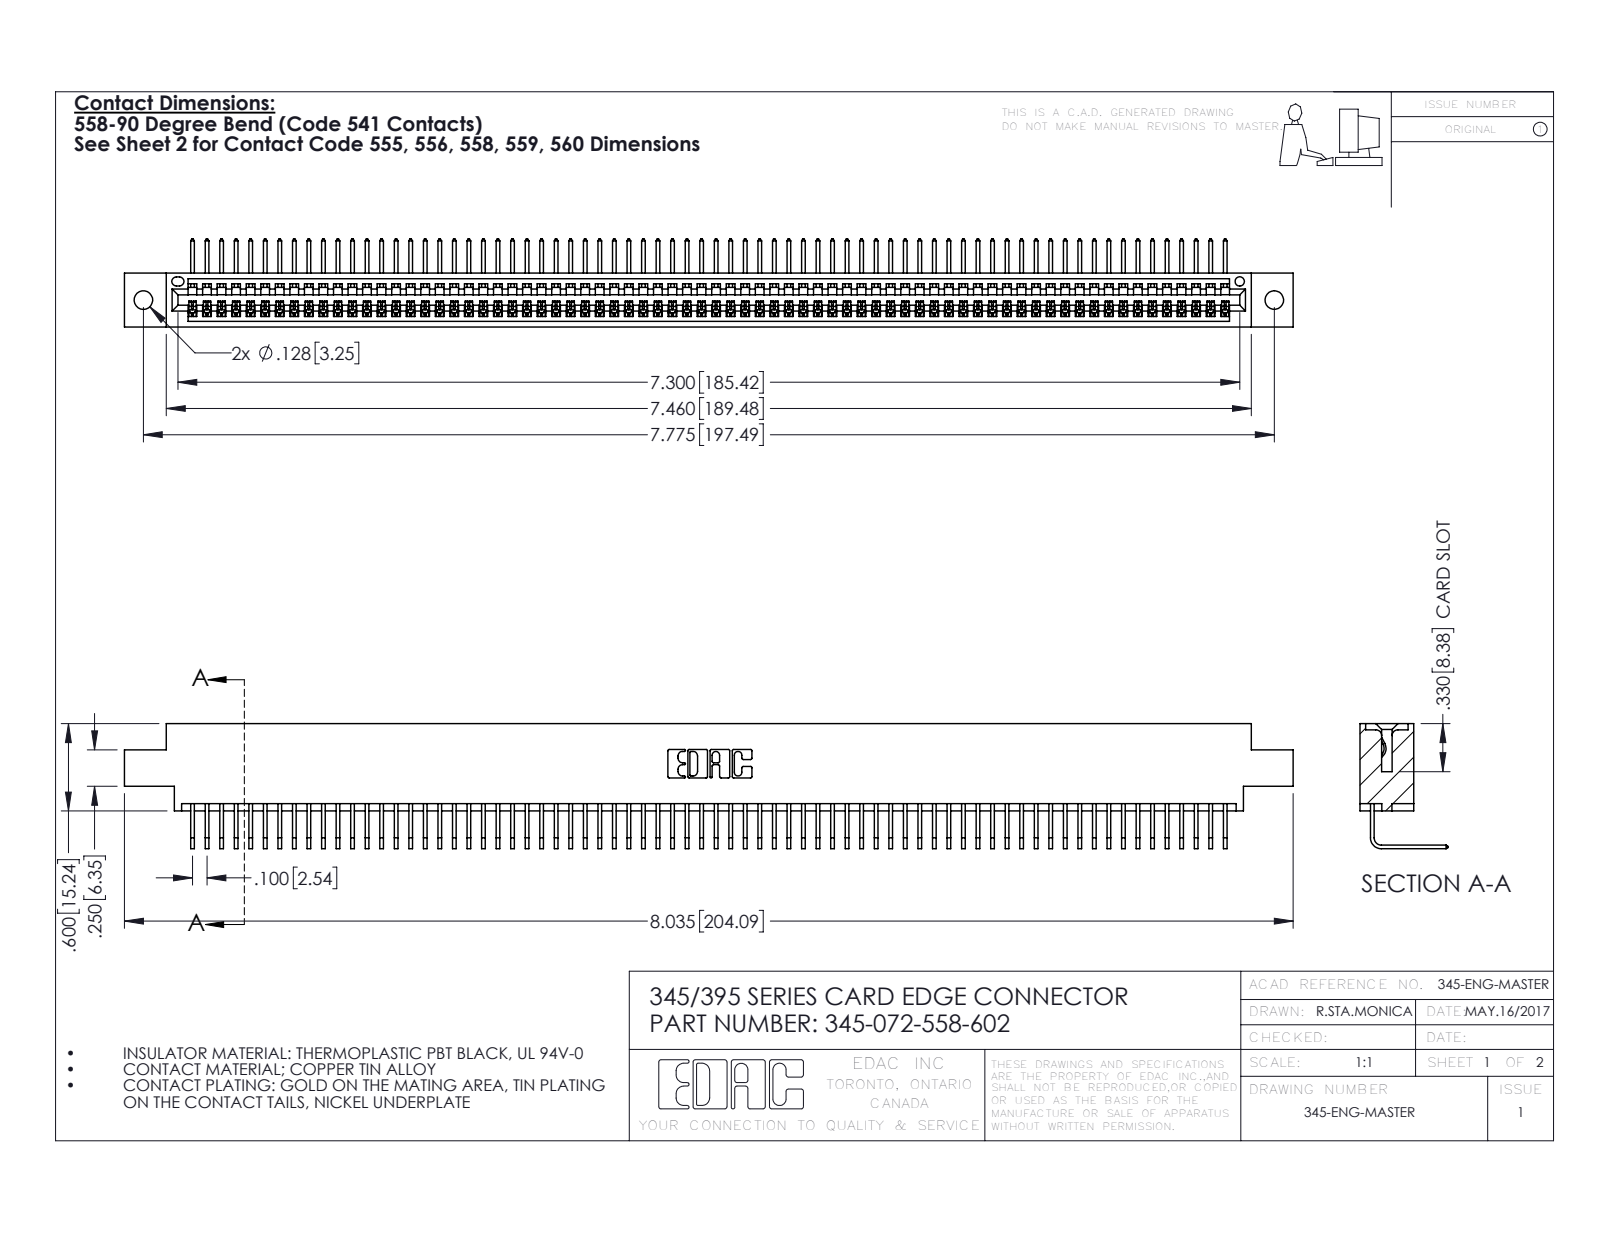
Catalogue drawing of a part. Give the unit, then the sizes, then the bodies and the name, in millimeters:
Units: millimetres
Overall size (bounding box): 204.1 × 21.8 × 15.4
Round holes (diameter × count): ⌀3.3 ×2, ⌀1.6 ×1
Partial cylindrical surfaces — rounded edges, fillets, slot ends (radius × count): R0.2 ×144, R0.3 ×22, R0.2 ×6, R0.8 ×6, R0.7 ×3, R0.8 ×2, R1 ×2, R0.4 ×1
Main face-to-face distances: 1.8, 7.6, 9.4, 5.1, 2.5, 6.9, 0.6, 5.7, 4.4, 3.8
Hole centre spacings: 6.9, 191.5, 197.5
Volume: 19 710 mm³ · Surface area: 27 880 mm²
Bodies: 73 solids, 4450 faces (3108 planar, 1342 cylindrical, 0 other)
Part name (STEP PRODUCT): 345-072-558-602; 345 Part_0.170 Offset - 0.128 Dia; 345-292-001_558 Tail - 2
STEP written by: SolidWorks 2016 (CONFIG_CONTROL_DESIGN)
